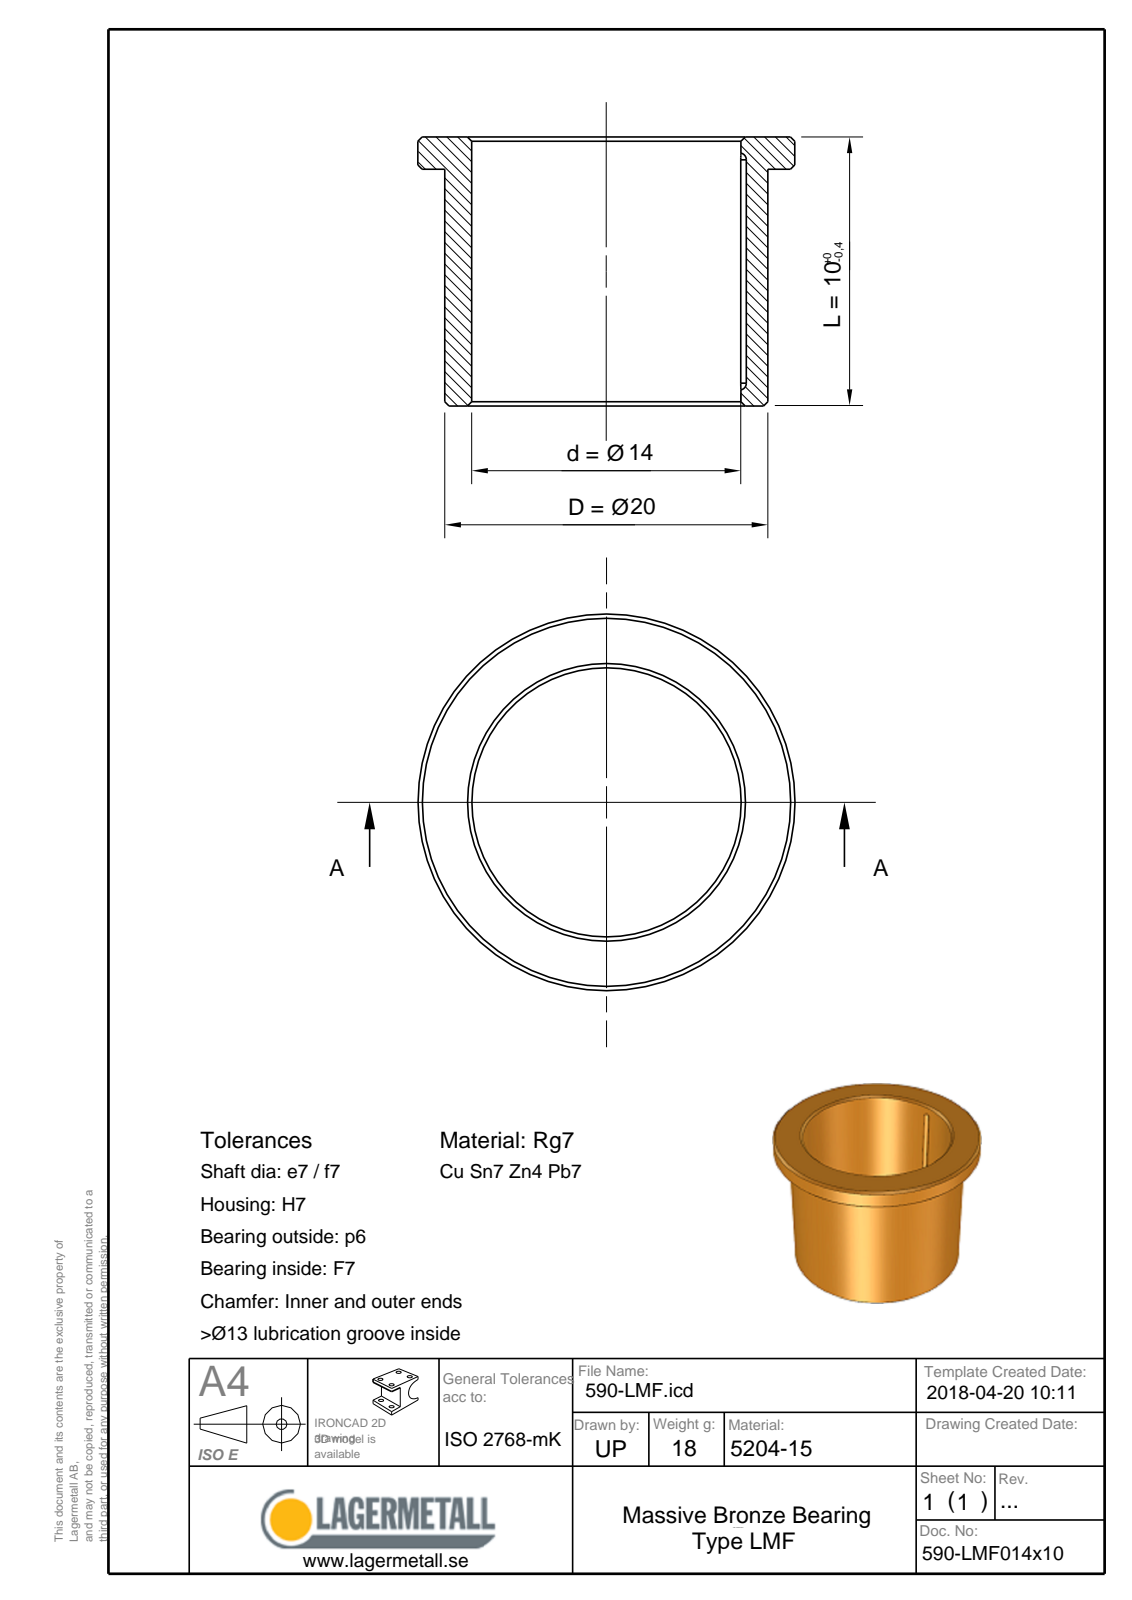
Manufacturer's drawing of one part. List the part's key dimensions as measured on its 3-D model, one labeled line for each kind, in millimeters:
Part name (STEP PRODUCT): 590-LMF014x10
STEP written by: Spatial InterOp 3D (CONFIG_CONTROL_DESIGN)
Units: millimetres
Bodies: 1 solid, 18 faces (5 planar, 6 cylindrical, 7 other)
Overall size (bounding box): 25 × 25 × 10
Volume: 2 089 mm³ · Surface area: 1 705 mm²
Round holes (diameter × count): ⌀14 ×1
Round bosses / shafts (diameter × count): ⌀25 ×1, ⌀20 ×1
Partial cylindrical surfaces — rounded edges, fillets, slot ends (radius × count): R0.75 ×3
Main face-to-face distances: 3, 7, 10, 1.5
